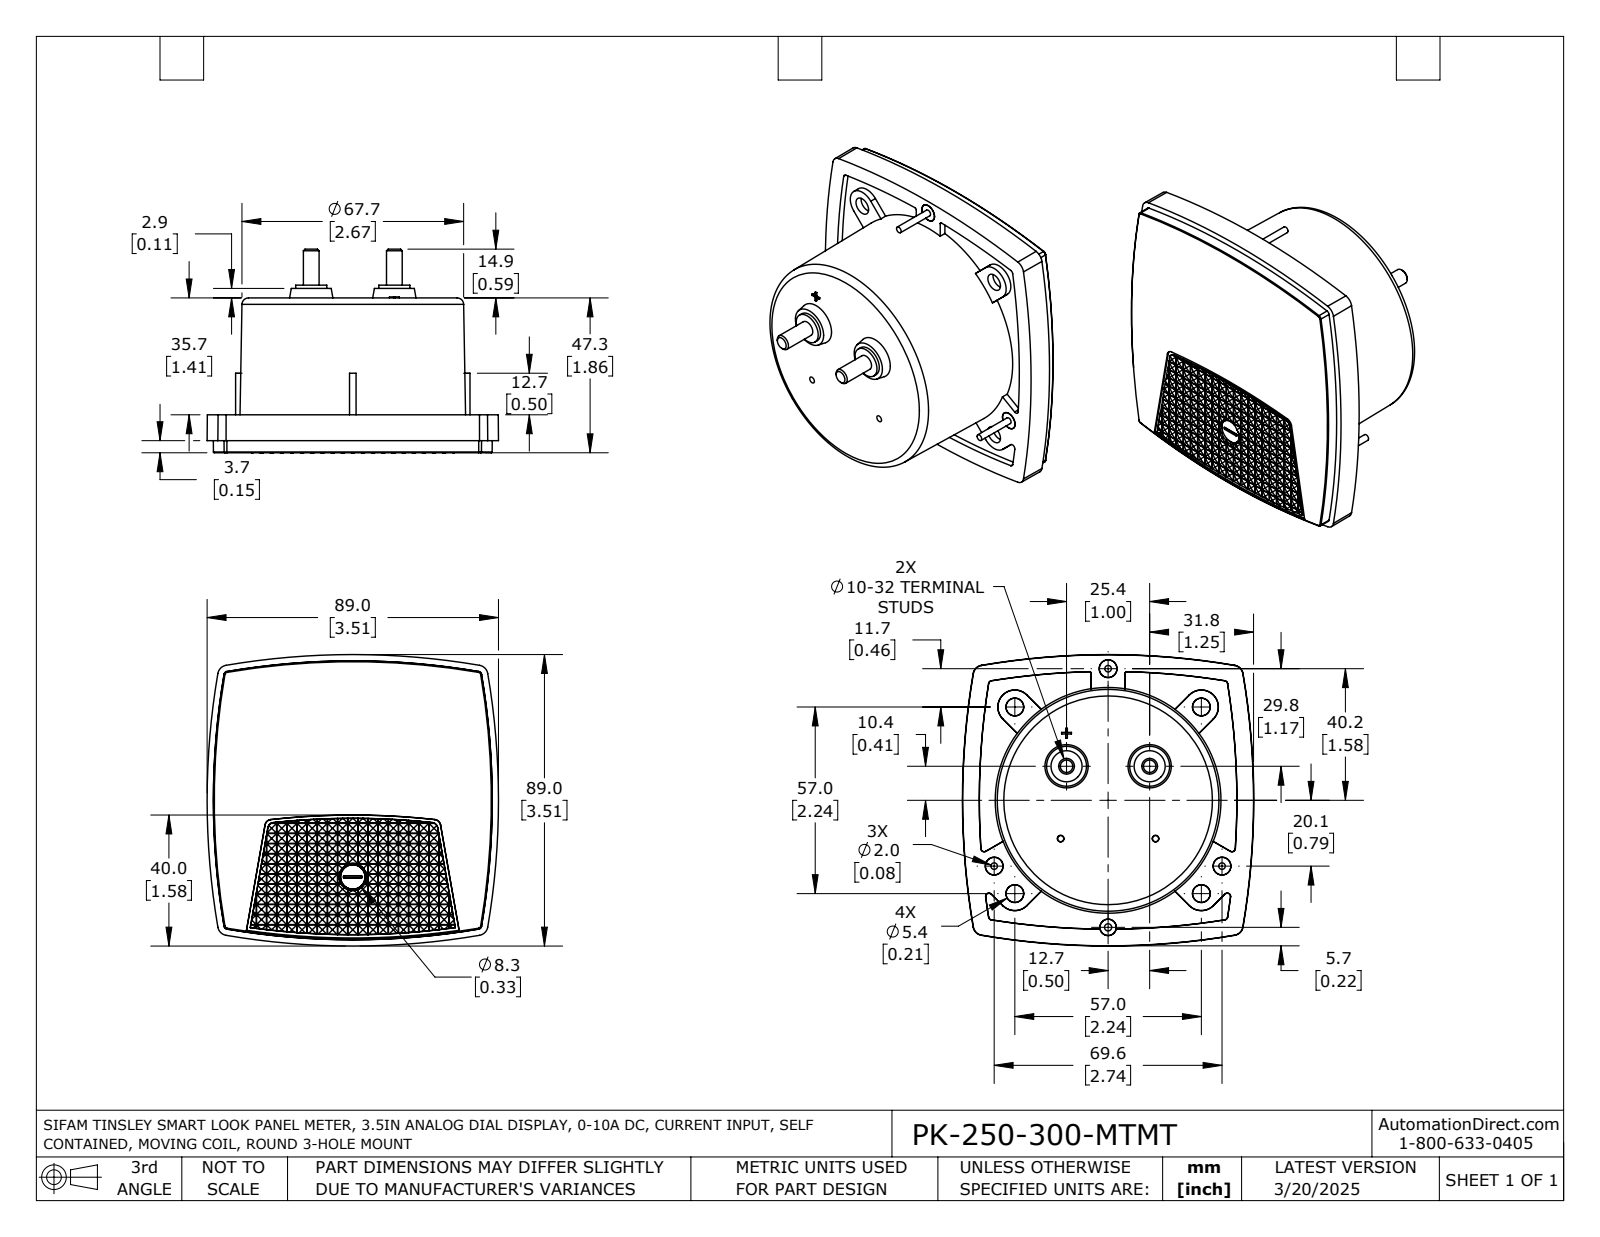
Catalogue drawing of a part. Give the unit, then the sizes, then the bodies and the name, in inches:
Units: inches
Overall size (bounding box): 3.505 × 3.505 × 2.453
Round holes (diameter × count): ⌀0.087 ×1
Round bosses / shafts (diameter × count): ⌀0.213 ×3, ⌀0.079 ×3, ⌀0.374 ×2, ⌀0.189 ×2
Partial cylindrical surfaces — rounded edges, fillets, slot ends (radius × count): R8.961 ×1
Main face-to-face distances: 1.862, 1.406, 0.457, 0.079, 1.484, 0.378, 0.024, 0.096, 0.072, 0.12
Volume: 12.99 in³ · Surface area: 44.29 in²
Bodies: 1 solid, 1078 faces (950 planar, 23 cylindrical, 105 other)
Part name (STEP PRODUCT): PK-250-300-MTMT
STEP written by: SolidWorks 2021 (AUTOMOTIVE_DESIGN)
